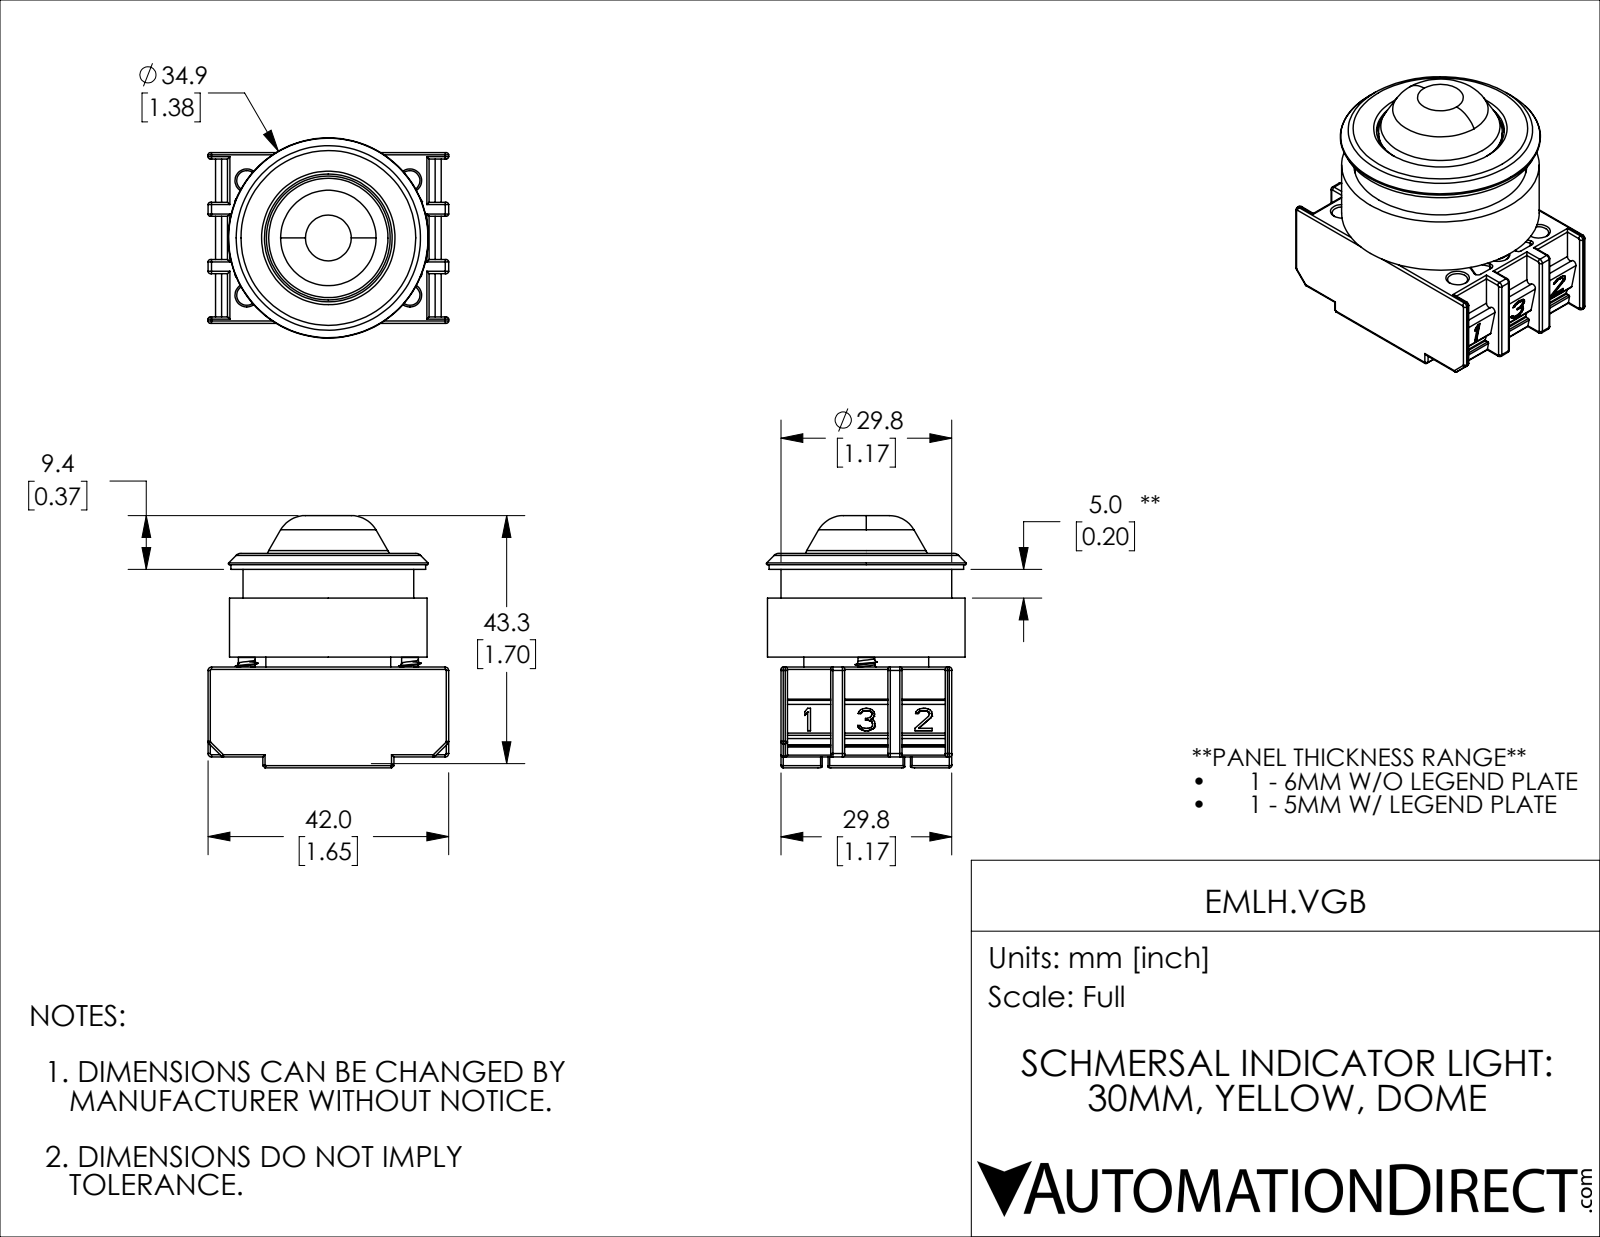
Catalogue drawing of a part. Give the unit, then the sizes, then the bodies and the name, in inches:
Units: inches
Overall size (bounding box): 1.734 × 1.654 × 1.375
Round holes (diameter × count): ⌀0.138 ×6, ⌀0.203 ×6, ⌀0.433 ×1, ⌀0.496 ×1, ⌀0.591 ×1, ⌀0.709 ×1, ⌀0.878 ×1, ⌀0.953 ×1, ⌀1.024 ×1, ⌀1.063 ×1, ⌀1.189 ×1
Round bosses / shafts (diameter × count): ⌀0.189 ×2, ⌀0.115 ×2, ⌀1.358 ×1, ⌀1.339 ×1, ⌀1.173 ×1, ⌀1.004 ×1, ⌀0.965 ×1, ⌀0.937 ×1
Partial cylindrical surfaces — rounded edges, fillets, slot ends (radius × count): R0.016 ×115, R0.012 ×48, R0.008 ×28, R0.024 ×8, R0.02 ×6, R0.004 ×2, R0.024 ×2, R0.031 ×2
Main face-to-face distances: 1.173, 0.069, 0.075, 0.762, 0.781, 0.713, 0.394, 0.134, 0.307, 0.173
Hole centre spacings: 0.394, 0.685, 1.189, 1.122, 0.561, 0.787, 1.371
Volume: 1.378 in³ · Surface area: 34.46 in²
Bodies: 3 solids, 1622 faces (641 planar, 498 cylindrical, 483 other)
Part name (STEP PRODUCT): EMLH.VGB
STEP written by: SolidWorks 2019 (CONFIG_CONTROL_DESIGN)
